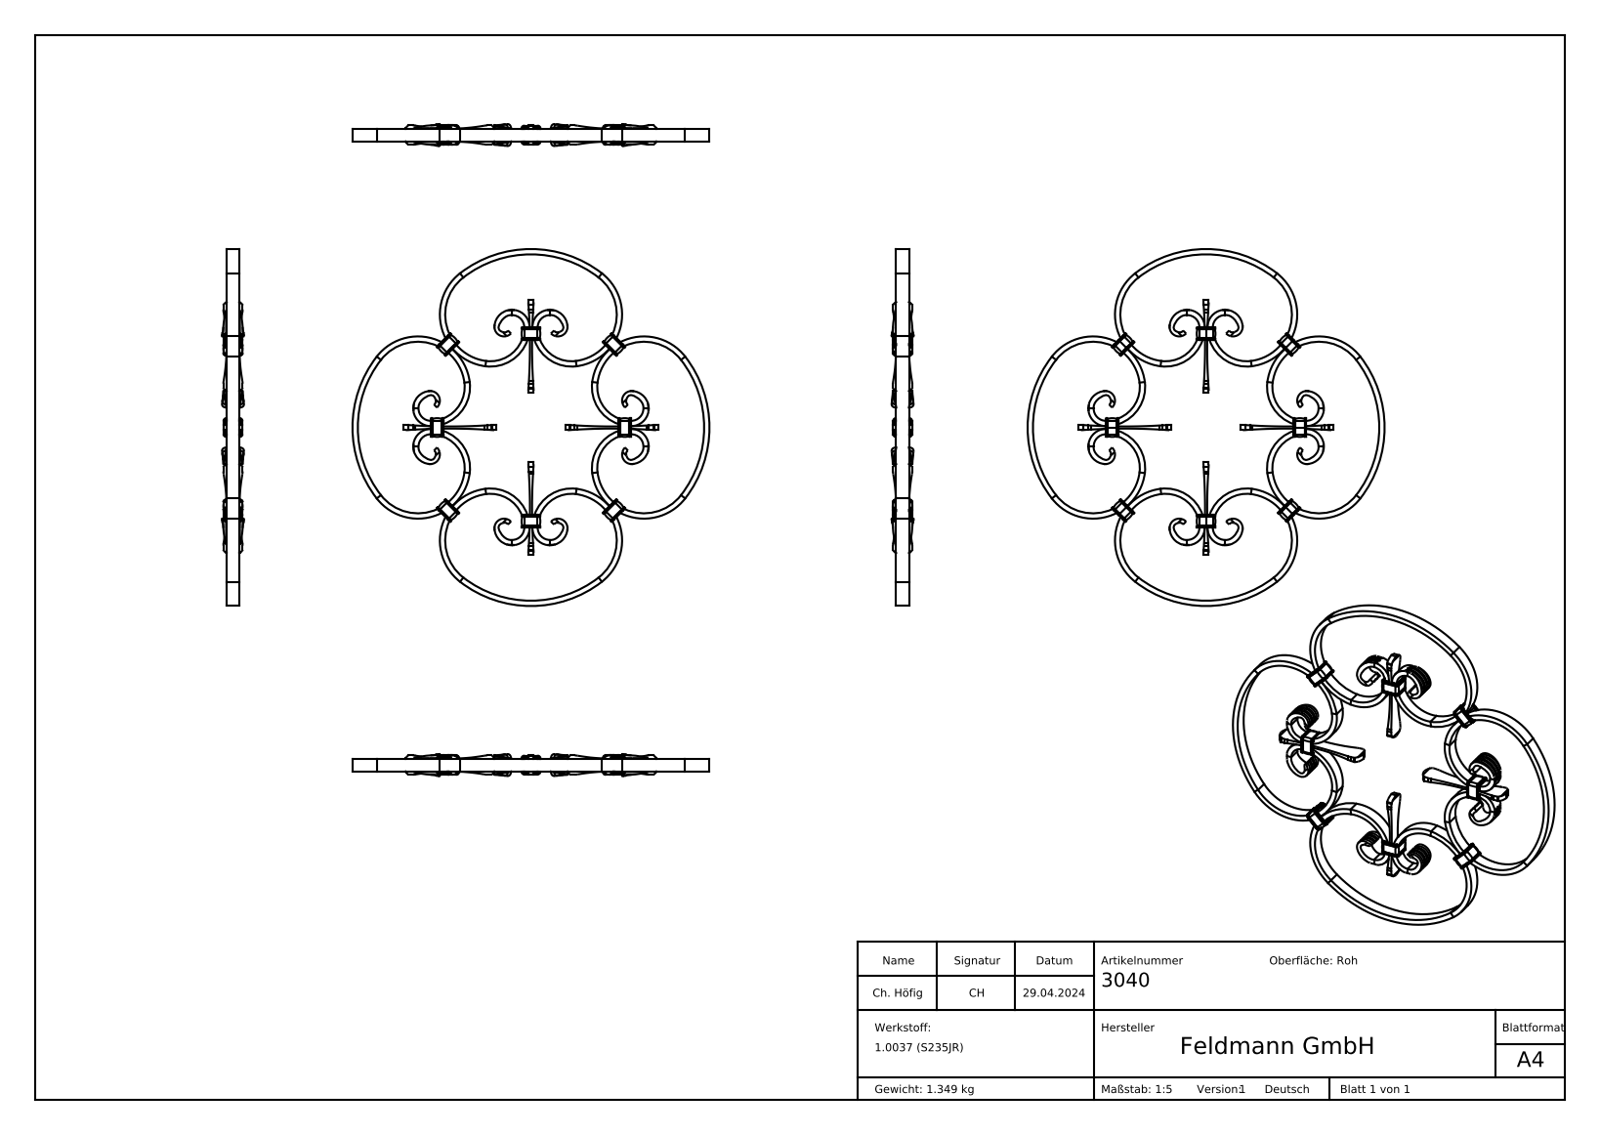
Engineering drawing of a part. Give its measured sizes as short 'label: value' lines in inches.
name: 3040
written by: SolidWorks 2018 (CONFIG_CONTROL_DESIGN)
unit: in
bodies: 12 solids, 1728 faces (608 planar, 592 cylindrical, 528 other)
size: 13.189 × 13.189 × 0.811
volume: 10.55 in³; area: 167.7 in²
rounds: 212× R0.02, 64× R0.004, 16× R0.039, 16× R0.118, 16× R0.472, 16× R0.541, 16× R0.546, 16× R0.591
face distances: 0.472, 0.484, 0.02, 0.512, 0.492, 0.504, 0.098, 0.496, 0.602, 0.61
